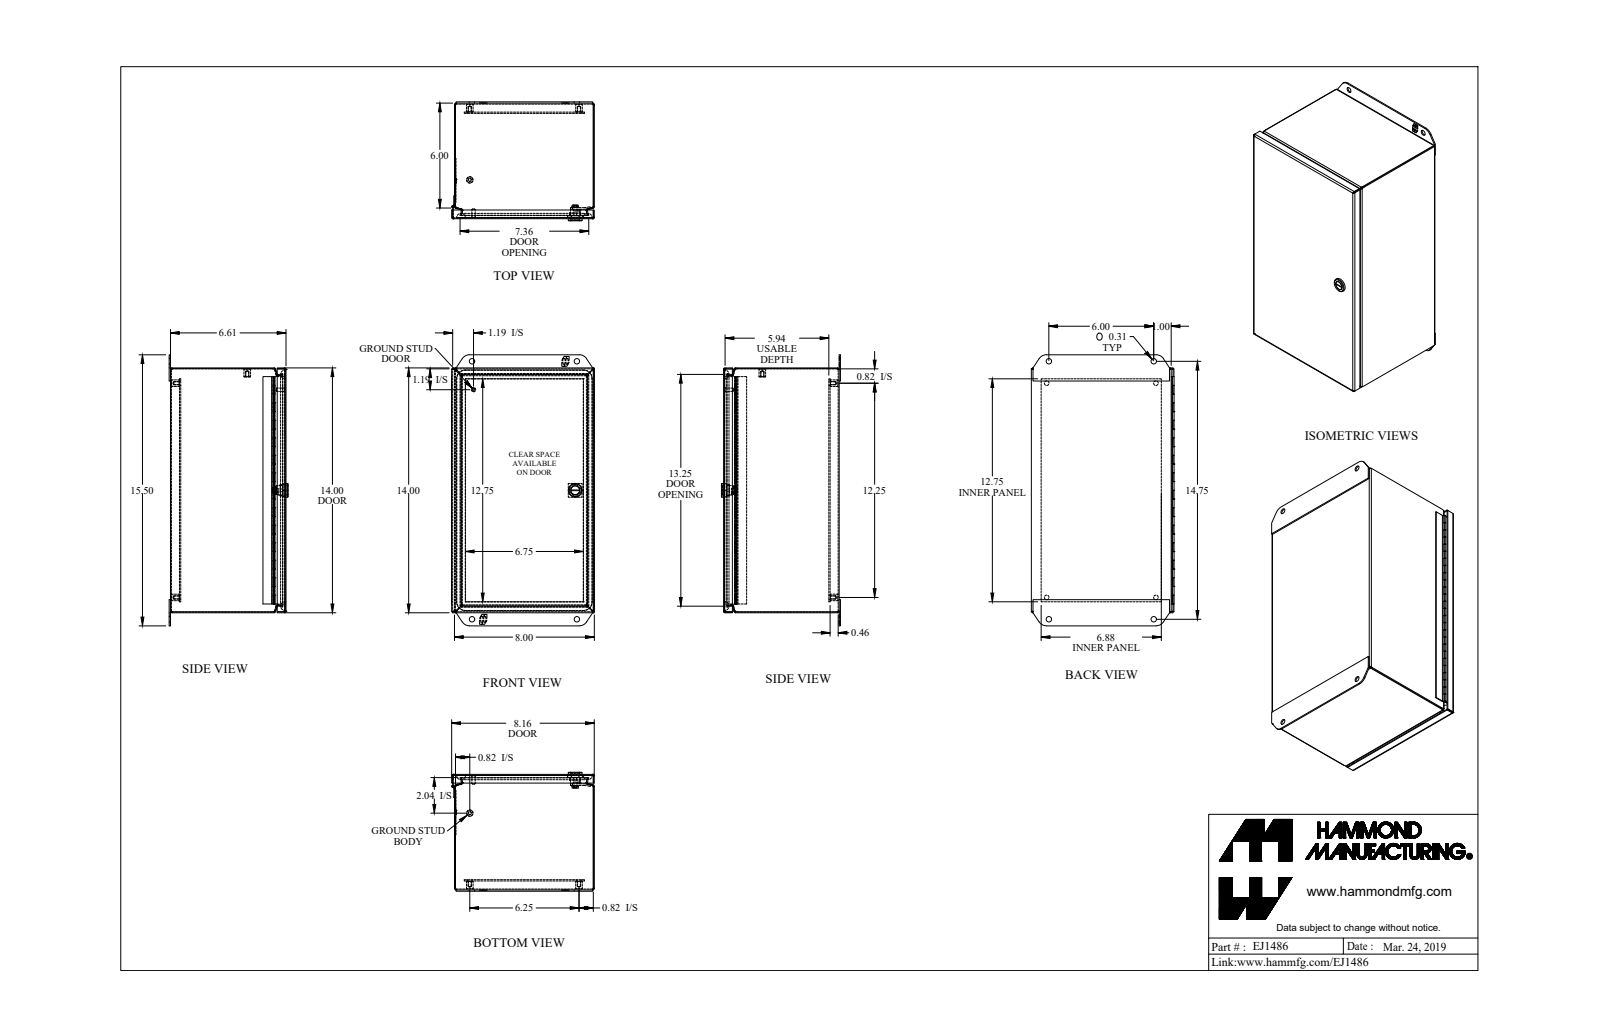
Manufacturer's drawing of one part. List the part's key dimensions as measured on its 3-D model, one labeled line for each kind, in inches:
Part name (STEP PRODUCT): EJ1486_Default
STEP written by: SolidWorks 2019 (CONFIG_CONTROL_DESIGN)
Units: inches
Bodies: 16 solids, 739 faces (409 planar, 238 cylindrical, 92 other)
Overall size (bounding box): 15.5 × 8.165 × 6.805
Volume: 43.32 in³ · Surface area: 1 440 in²
Round holes (diameter × count): ⌀0.156 ×5, ⌀0.265 ×4, ⌀0.313 ×4, ⌀0.05 ×1, ⌀0.516 ×1
Round bosses / shafts (diameter × count): ⌀0.375 ×5, ⌀0.788 ×1, ⌀0.535 ×1, ⌀0.496 ×1, ⌀0.435 ×1, ⌀0.25 ×1, ⌀0.188 ×1, ⌀0.1 ×1
Partial cylindrical surfaces — rounded edges, fillets, slot ends (radius × count): R0.029 ×16, R0.086 ×16, R0.281 ×10, R0.25 ×4, R0.499 ×4, R0.5 ×4, R0.06 ×2, R0.539 ×2
Main face-to-face distances: 0.057, 6.554, 7.943, 6.611, 0.072, 0.589, 6.497, 13.943, 0.46, 0.517
Hole centre spacings: 14.824, 1.256, 1.257, 6, 6.129, 6.25, 6.251, 6.252
